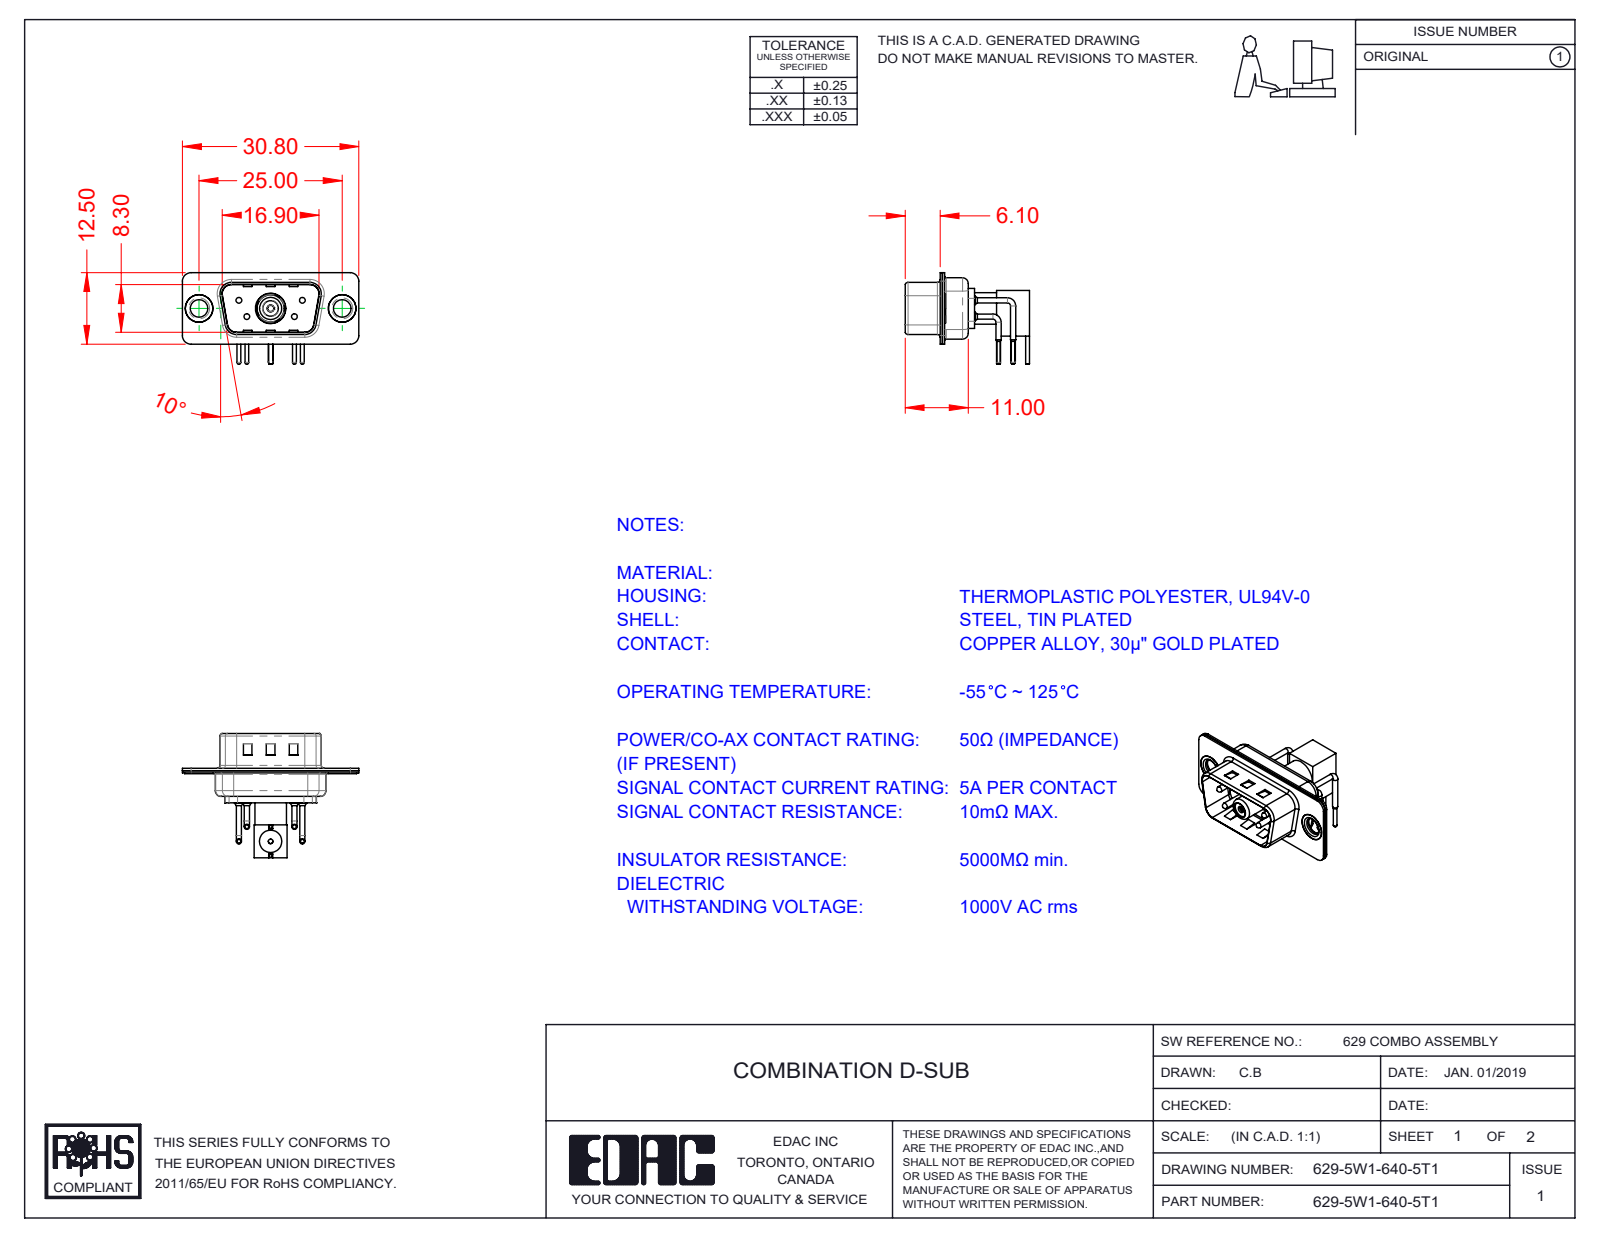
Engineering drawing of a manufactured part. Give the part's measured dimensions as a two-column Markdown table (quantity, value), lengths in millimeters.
| quantity | value |
| --- | --- |
| part name | 629Combo Thru Hole Rivet; 629Combo Contact Row 2; RA Back Shell; Locking Collar (+8 more) |
| STEP written by | SolidWorks 2020 (CONFIG_CONTROL_DESIGN) |
| units | millimeters |
| bodies | 16 solids, 870 faces (420 planar, 324 cylindrical, 126 other) |
| overall size | 30.8 × 21.71 × 16 |
| volume | 1 549 mm³ |
| surface area | 4 471 mm² |
| round holes (diameter × count) | 1.6 × 5, 0.75 × 4, 2 × 4, 3.05 × 2, 4 × 2, 4.8 × 2, 0.8 × 1, 1.1 × 1, 1.2 × 1, 1.5 × 1, 2.5 × 1, 2.7 × 1 |
| round bosses / shafts (diameter × count) | 0.9 × 8, 1.5 × 4, 1 × 4, 0.65 × 4, 5 × 2, 4.9 × 2, 3.55 × 2, 0.8 × 2 |
| partial cylindrical surfaces (radius × count) | 1.5 × 16, 2 × 12, 0.5 × 8, 1.6 × 8, 0.25 × 4, 0.6 × 4, 0.65 × 4, 0.9 × 4 |
| main face-to-face distances | 0.4, 0.8, 9.5, 0.65, 9.1, 0.35, 8.7, 9.9, 1.4, 5.75 |
| hole center spacings | 3.16, 5.72, 7.1, 12.5, 18.1, 4.39, 4.4, 8.31 |
